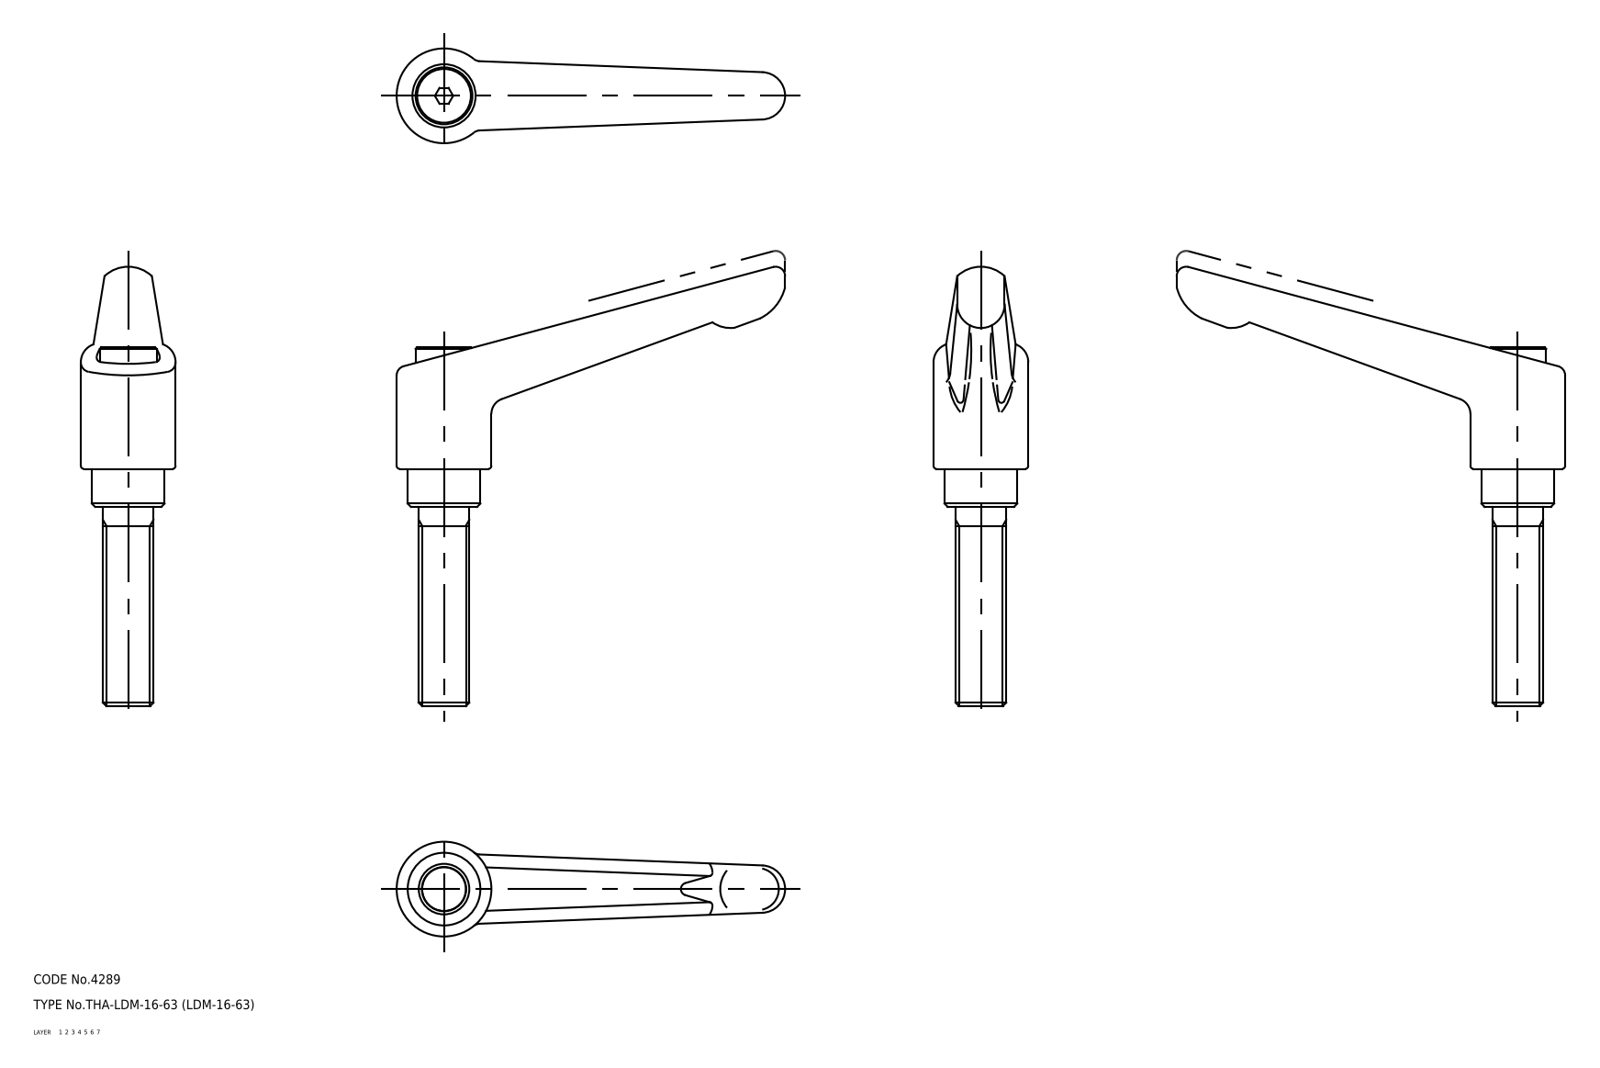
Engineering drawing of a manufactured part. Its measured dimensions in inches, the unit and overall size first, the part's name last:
Units: inches
Overall size (bounding box): 5.472 × 4.843 × 1.181
Volume: 3.55 in³ · Surface area: 31.85 in²
Bodies: 3 solids, 92 faces (0 planar, 0 cylindrical, 92 other)
Part name (STEP PRODUCT): sleeve; screw; handle; LDM_16_63_12486_36
STEP written by: CADfix (AUTOMOTIVE_DESIGN)
